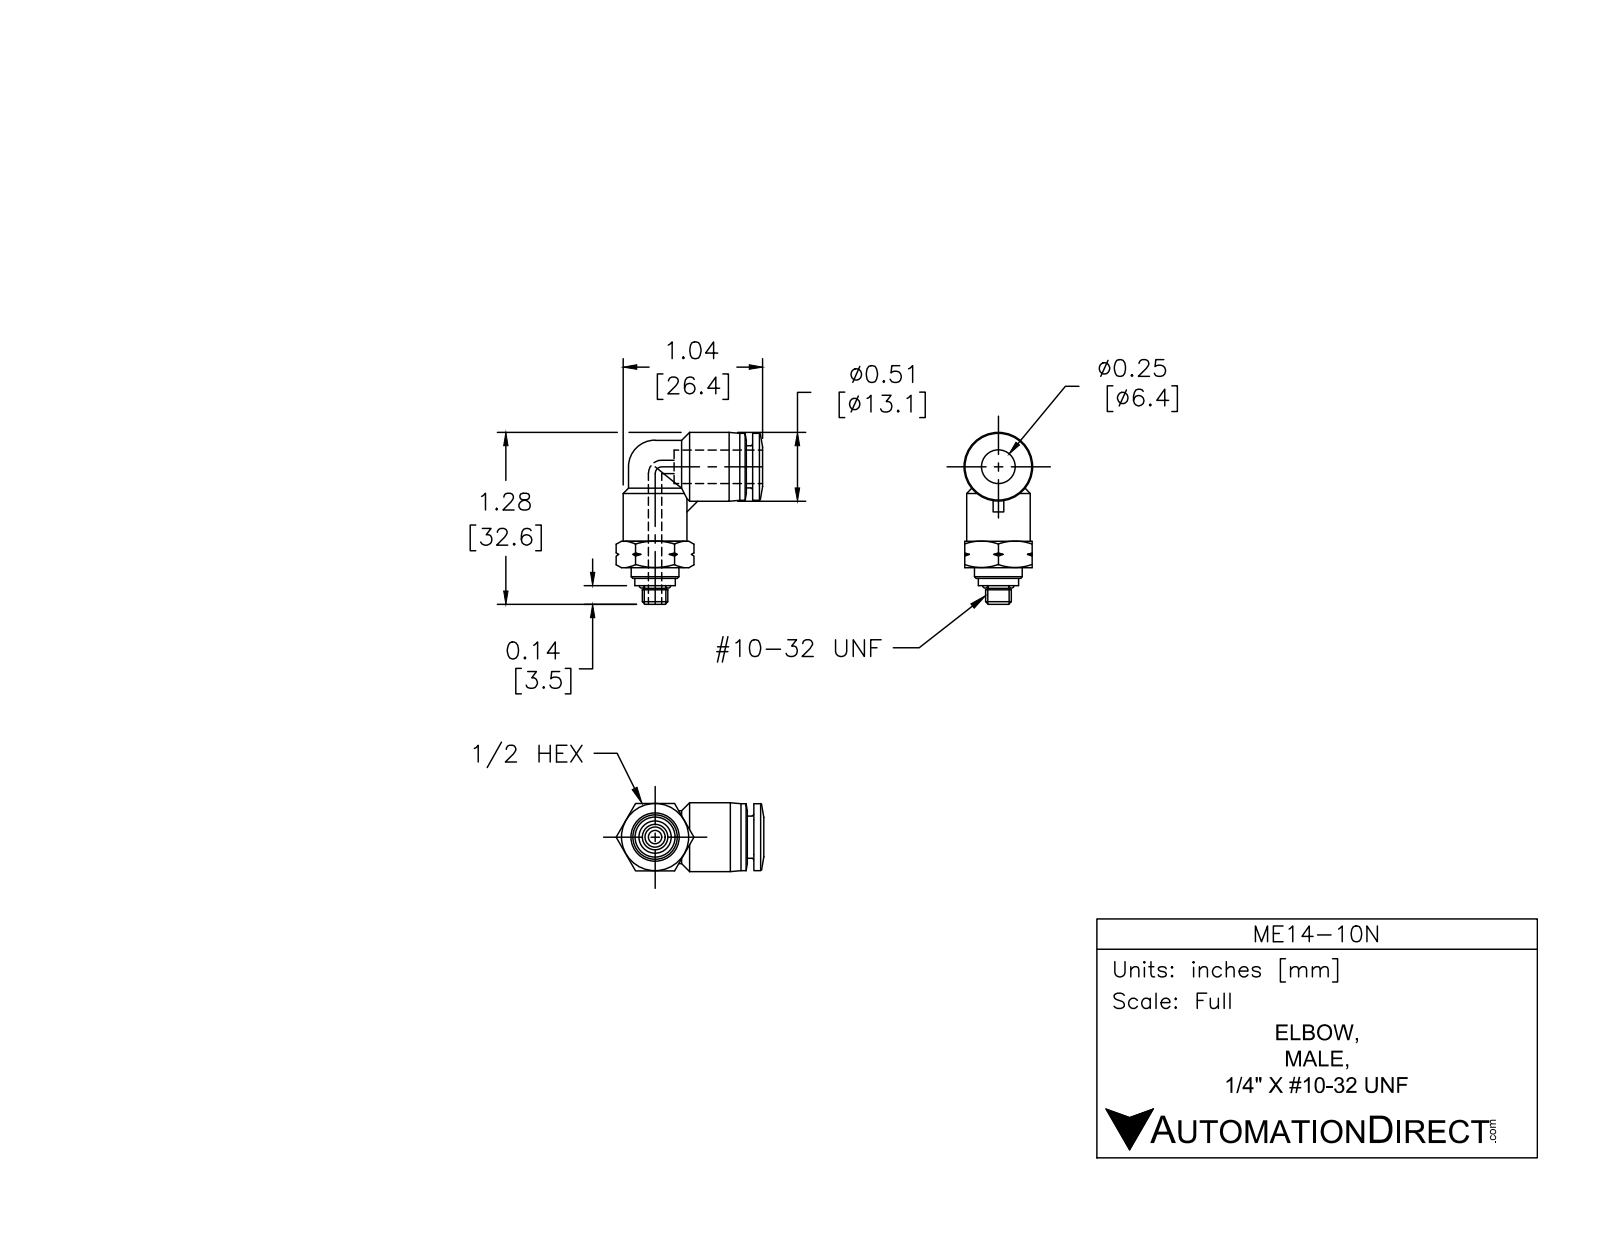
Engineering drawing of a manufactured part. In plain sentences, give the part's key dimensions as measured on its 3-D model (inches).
The part is named "ME14-10N". Its 3-D file was written by "SolidWorks 2015 (AUTOMOTIVE_DESIGN)". It is 2 solids with 108 faces: 19 planar, 30 cylindrical and 59 other. Overall it measures 1.276 by 1.096 by 0.512 inches. Its volume is 0.237 cubic inches and its surface area 4.142 square inches. Round holes: 2 of diameter 0.098, 1 of diameter 0.258. Round bosses or shafts: 2 of diameter 0.394, 1 of diameter 0.512, 1 of diameter 0.496, 1 of diameter 0.472, 1 of diameter 0.354, 1 of diameter 0.313, 1 of diameter 0.299, 1 of diameter 0.19. The main face-to-face distances are 0.5, 0.047, 0.539, 0.587, 0.102, 0.299, 0.197, 0.079, 0.024, 0.276.
